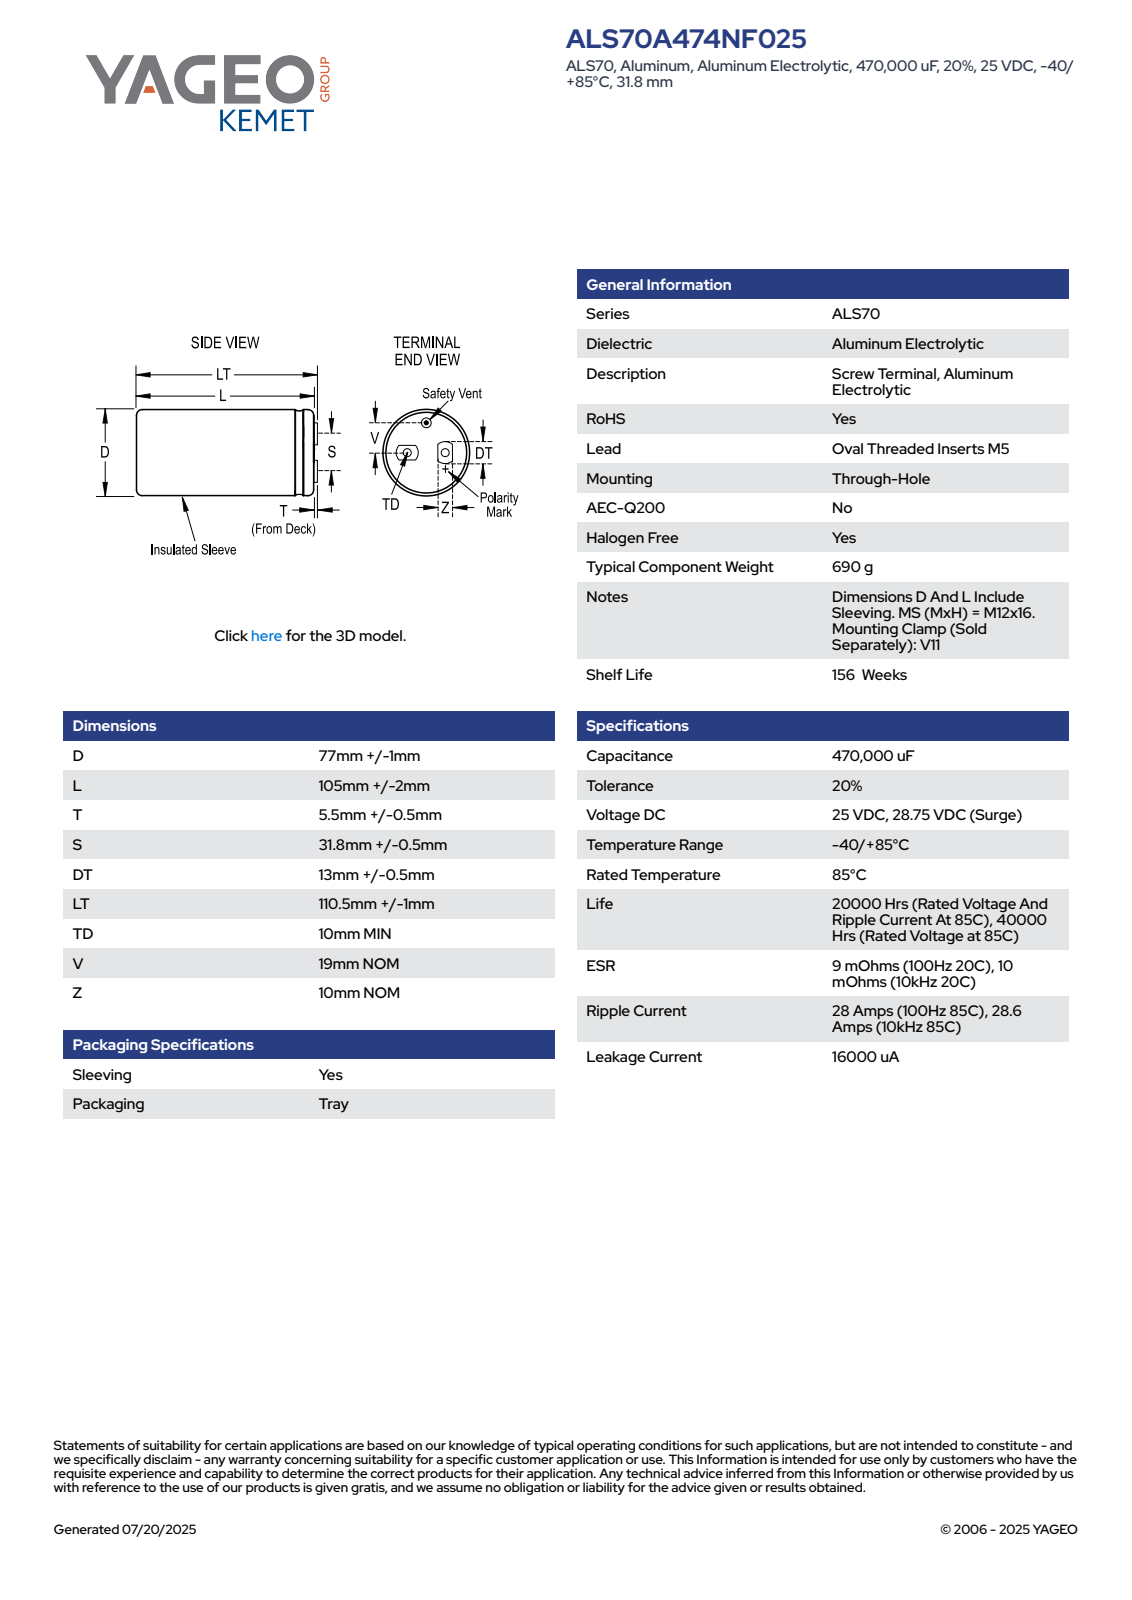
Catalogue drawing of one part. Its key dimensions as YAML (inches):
part_name: "CARC_KALSO_77X105_D78L107T6S31.8LT111.50V19.000"
step_written_by: "SolidWorks 2014 (AUTOMOTIVE_DESIGN)"
units: inches
bodies: {solids: 1, faces: 109, planar: 40, cylindrical: 30, other: 39}
overall_size: [4.409, 3.071, 3.071]
volume: 30.89
surface_area: 57.34
round_holes:
  - {diameter: 0.197, count: 2}
  - {diameter: 0.079, count: 1}
  - {diameter: 2.913, count: 1}
round_bosses_or_shafts:
  - {diameter: 0.669, count: 2}
  - {diameter: 3.071, count: 1}
  - {diameter: 0.118, count: 1}
partial_cylinders:
  - {radius: 0.315, count: 4}
  - {radius: 1.535, count: 1}
face_to_face_distances: [4.173, 4.193, 0.02, 4.409, 0.236, 0.217, 0.394, 4.016, 0.157, 0.177]
hole_center_spacings: [0.626, 0.976, 0.748, 1.252]
